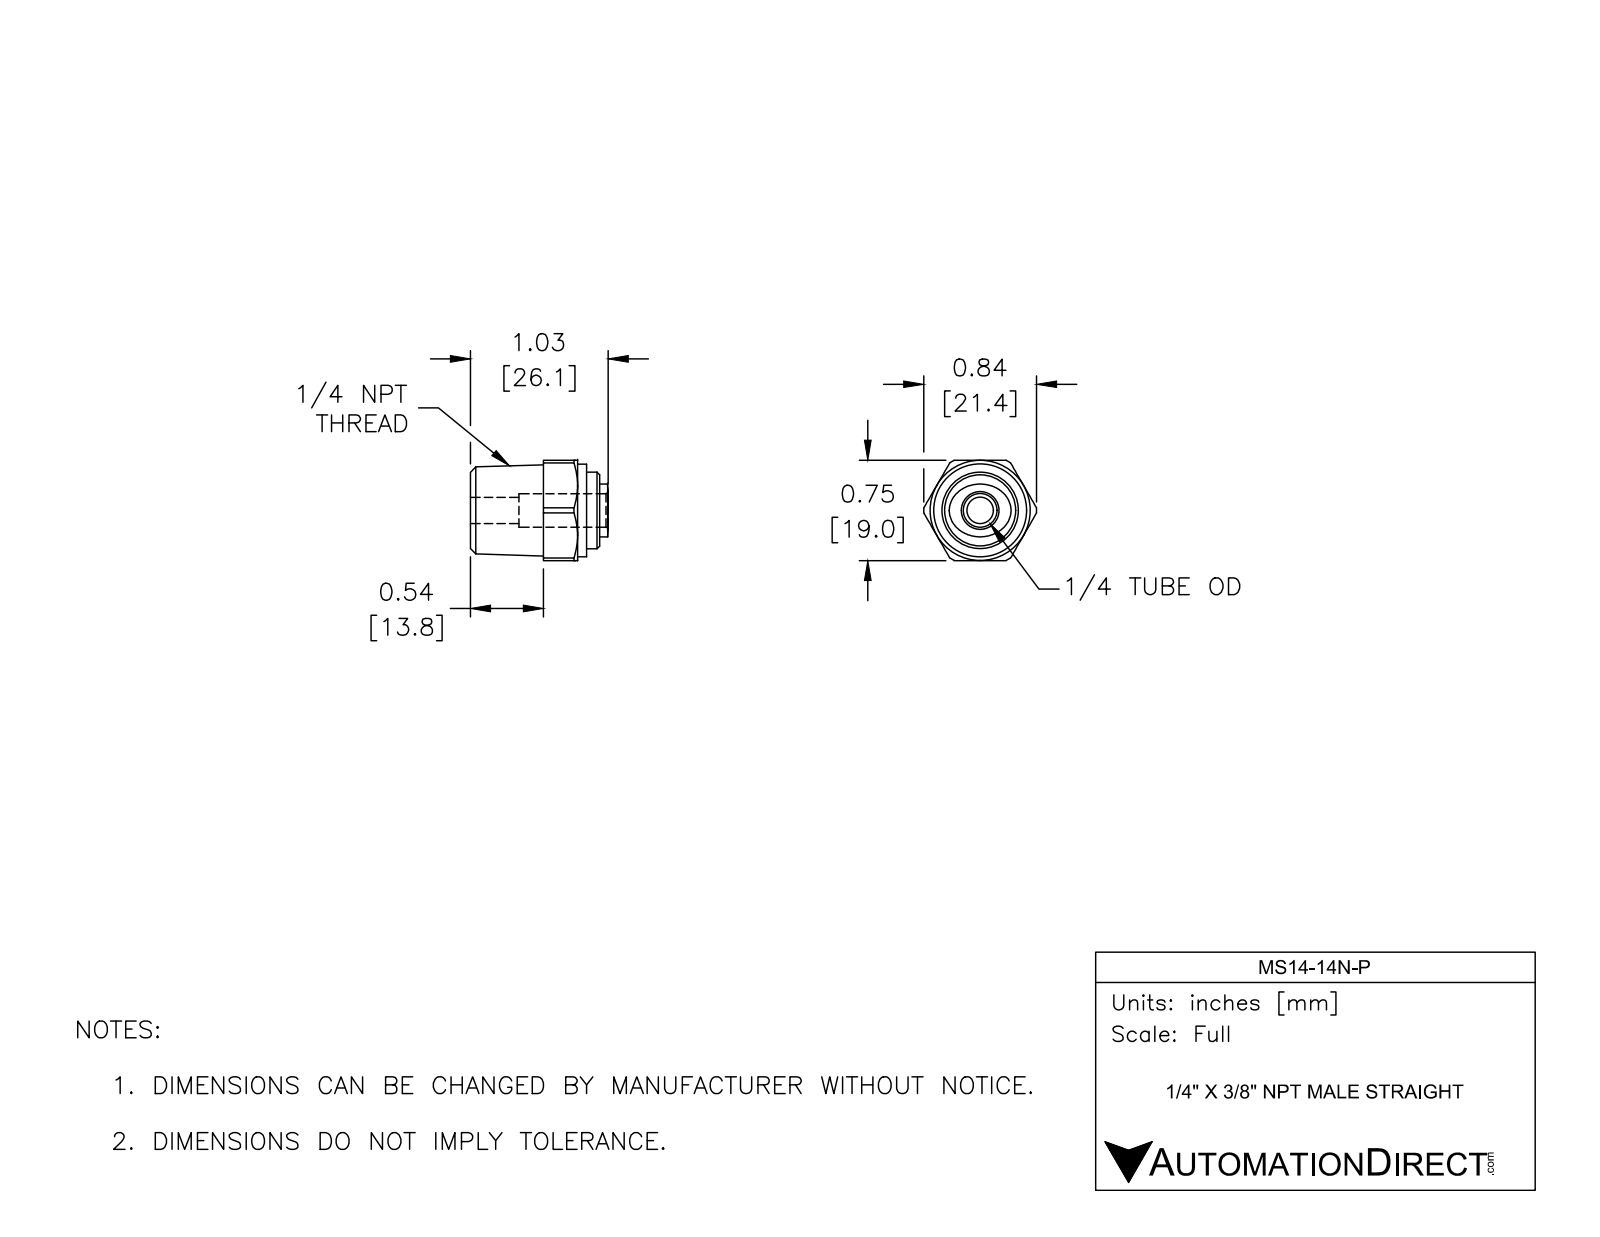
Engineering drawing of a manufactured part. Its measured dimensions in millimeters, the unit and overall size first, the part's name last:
Units: millimetres
Overall size (bounding box): 26.1 × 21.4 × 19
Round holes (diameter × count): ⌀5 ×1, ⌀6.4 ×1
Round bosses / shafts (diameter × count): ⌀17.6 ×1, ⌀14.5 ×1
Partial cylindrical surfaces — rounded edges, fillets, slot ends (radius × count): R10.7 ×1
Main face-to-face distances: 19, 22, 13.8, 8.2, 24.5, 10.7, 2.5, 20.3, 6.5, 1.7
Volume: 5 330 mm³ · Surface area: 2 394 mm²
Bodies: 1 solid, 46 faces (12 planar, 15 cylindrical, 19 other)
Part name (STEP PRODUCT): MS14-38N-P
STEP written by: SolidWorks 2017 (AUTOMOTIVE_DESIGN)
